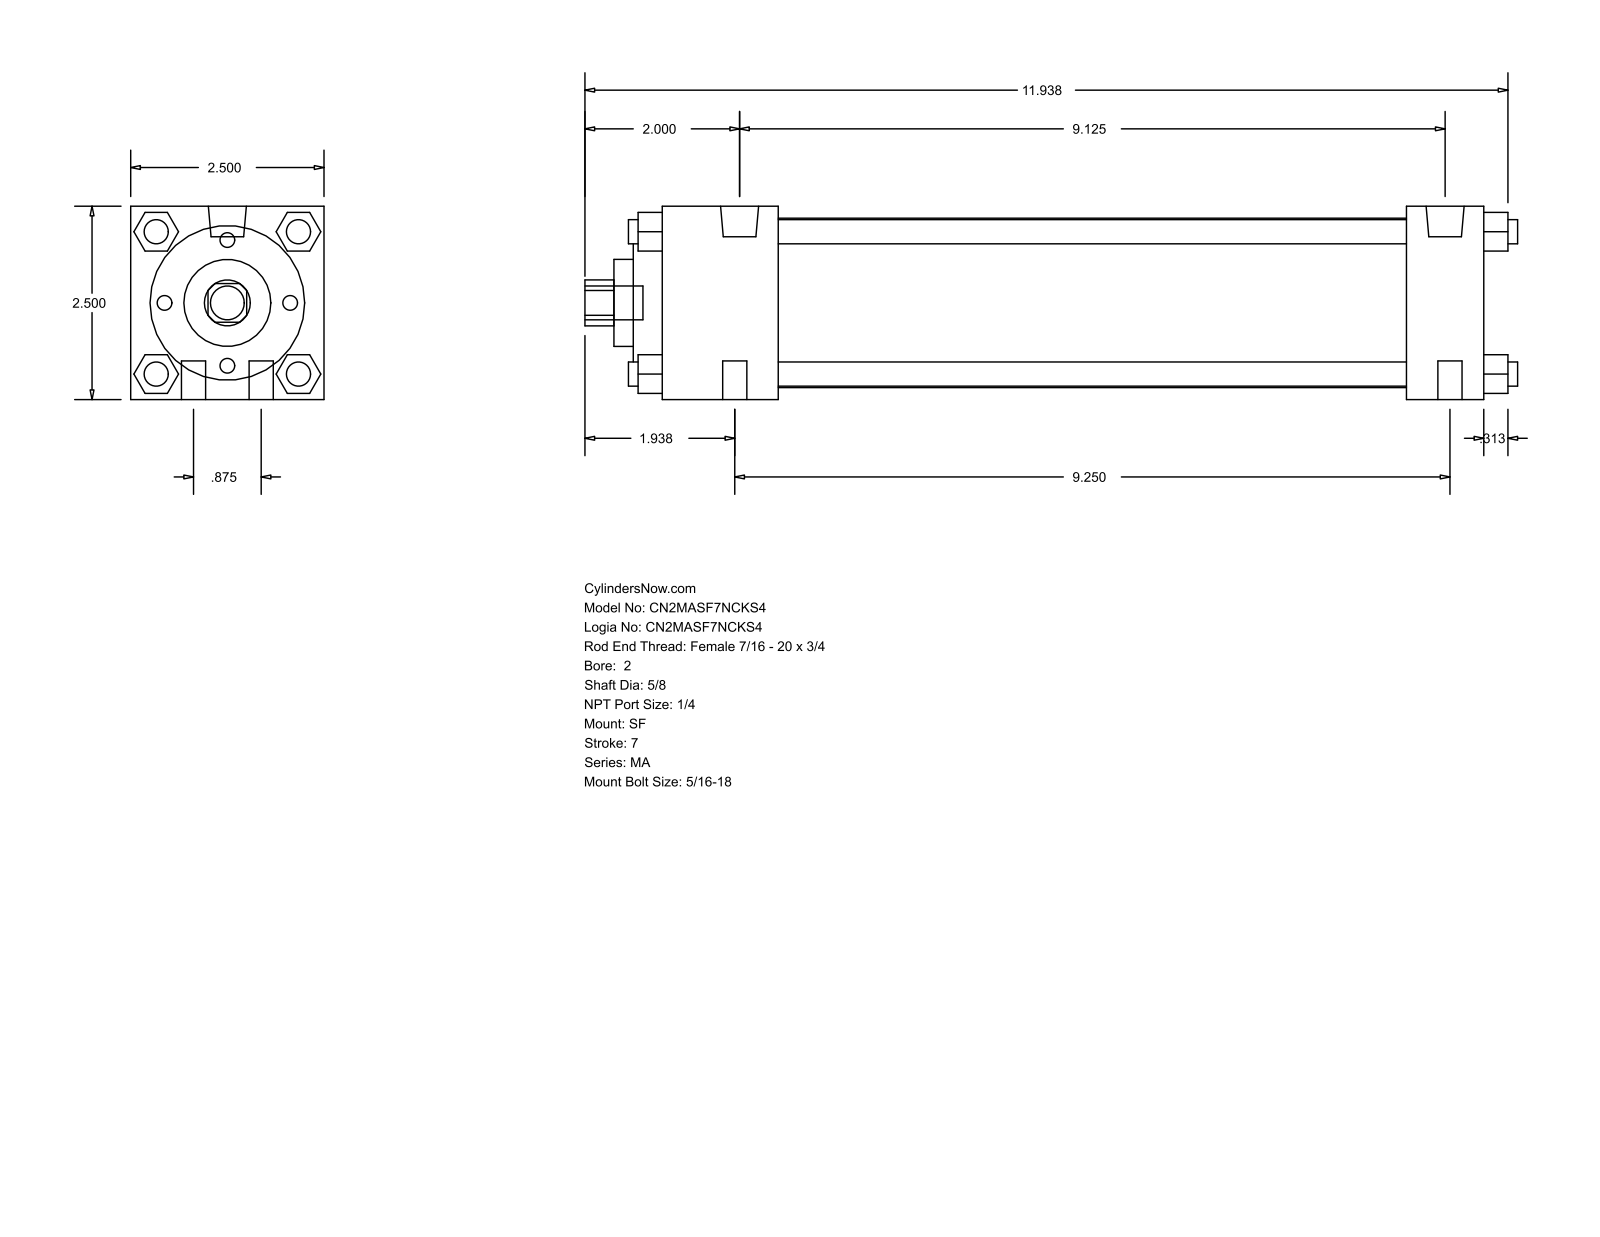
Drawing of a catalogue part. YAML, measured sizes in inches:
part_name: "MA_SF__0200_0.625"
step_written_by: "GSSL Pune (CONFIG_CONTROL_DESIGN)"
units: inches
bodies: {solids: 0, faces: 126, planar: 95, cylindrical: 31, other: 0}
overall_size: [12.063, 2.5, 2.5]
round_holes:
  - {diameter: 0.625, count: 1}
  - {diameter: 1.125, count: 1}
  - {diameter: 2, count: 1}
  - {diameter: 2.19, count: 1}
round_bosses_or_shafts:
  - {diameter: 0.313, count: 10}
  - {diameter: 0.492, count: 2}
  - {diameter: 0.437, count: 1}
partial_cylinders:
  - {radius: 0.297, count: 1}
face_to_face_distances: [2.5, 0.5, 1.5, 0.375, 10.625, 9.625, 1, 8.125, 9.125, 1.875]
